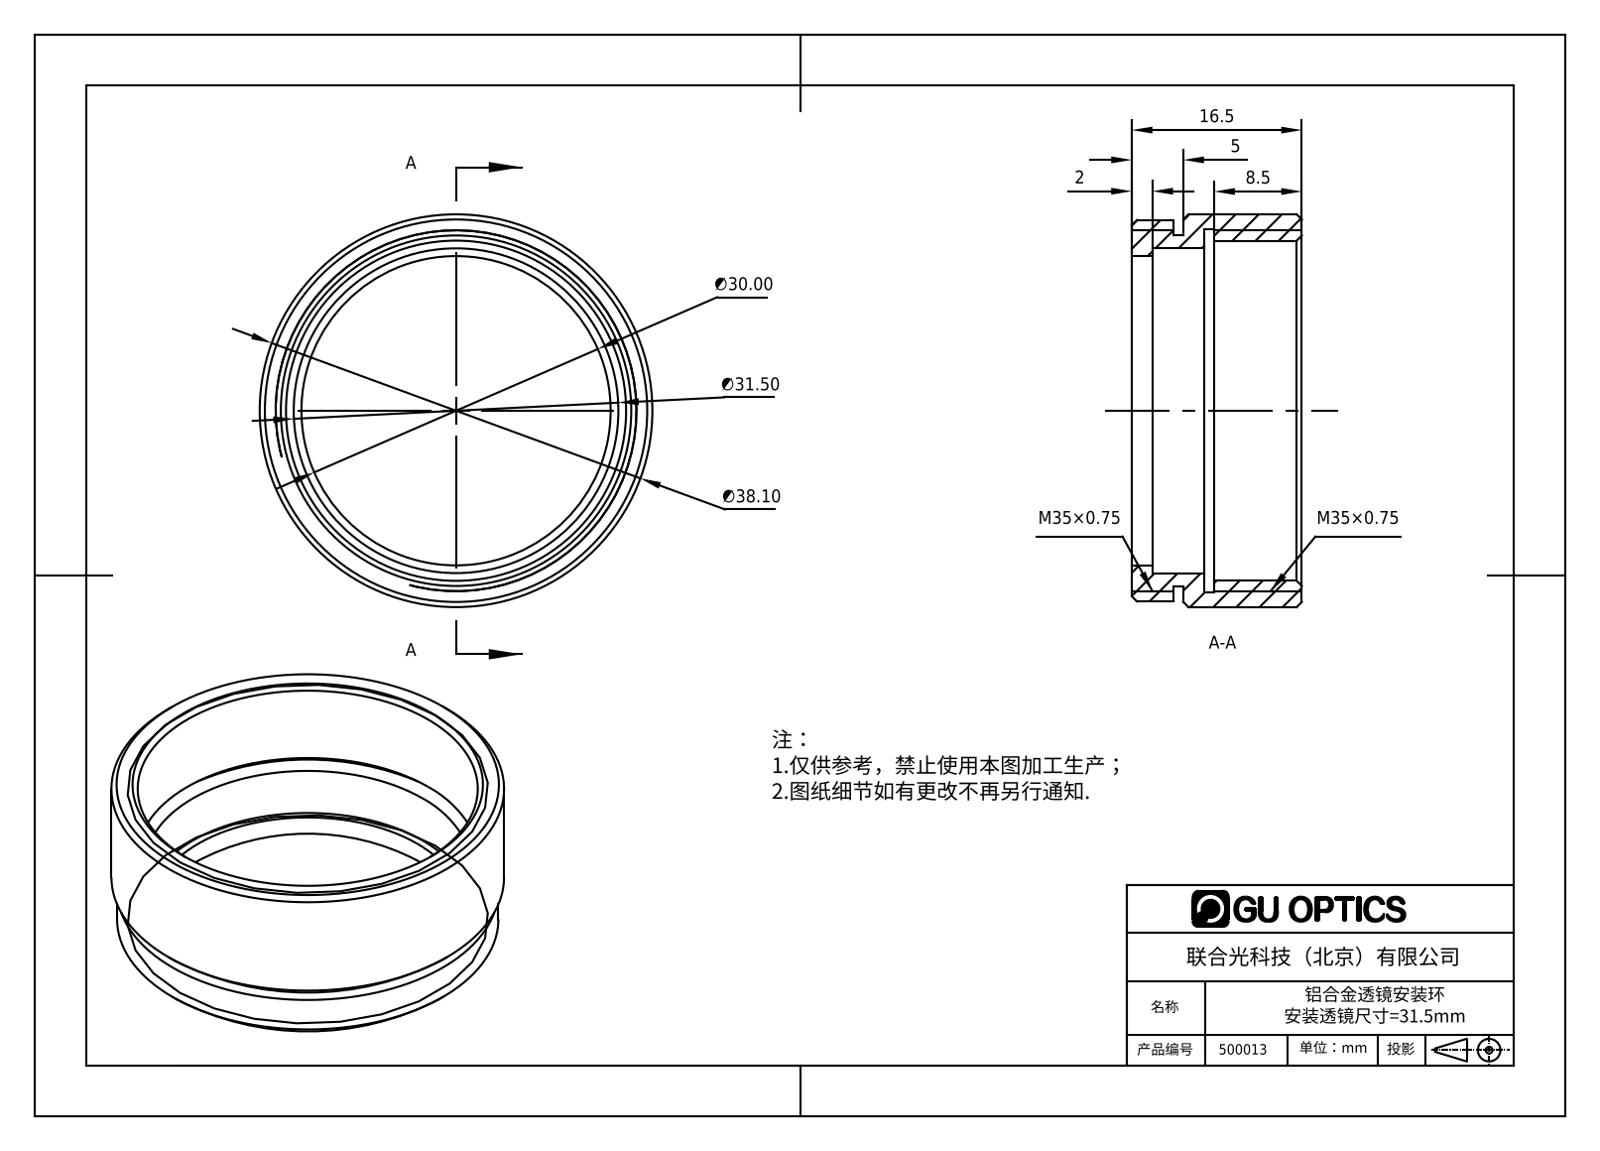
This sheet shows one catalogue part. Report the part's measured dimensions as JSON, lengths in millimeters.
{"part_name": "500013", "step_written_by": "SolidWorks 2016 (AUTOMOTIVE_DESIGN)", "units": "millimeters", "bodies": {"solids": 1, "faces": 29, "planar": 7, "cylindrical": 14, "other": 8}, "overall_size": [38.1, 38.1, 16.5], "volume_mm3": 4709, "surface_area_mm2": 4925, "round_holes": [[30, 1], [31.5, 1], [33, 1], [35.2, 1]], "round_bosses_or_shafts": [[38.1, 1], [37, 1], [34, 1]], "face_to_face_distances": [3, 2, 4, 1, 5, 7, 16.5, 9.5, 11.5, 12.5]}
